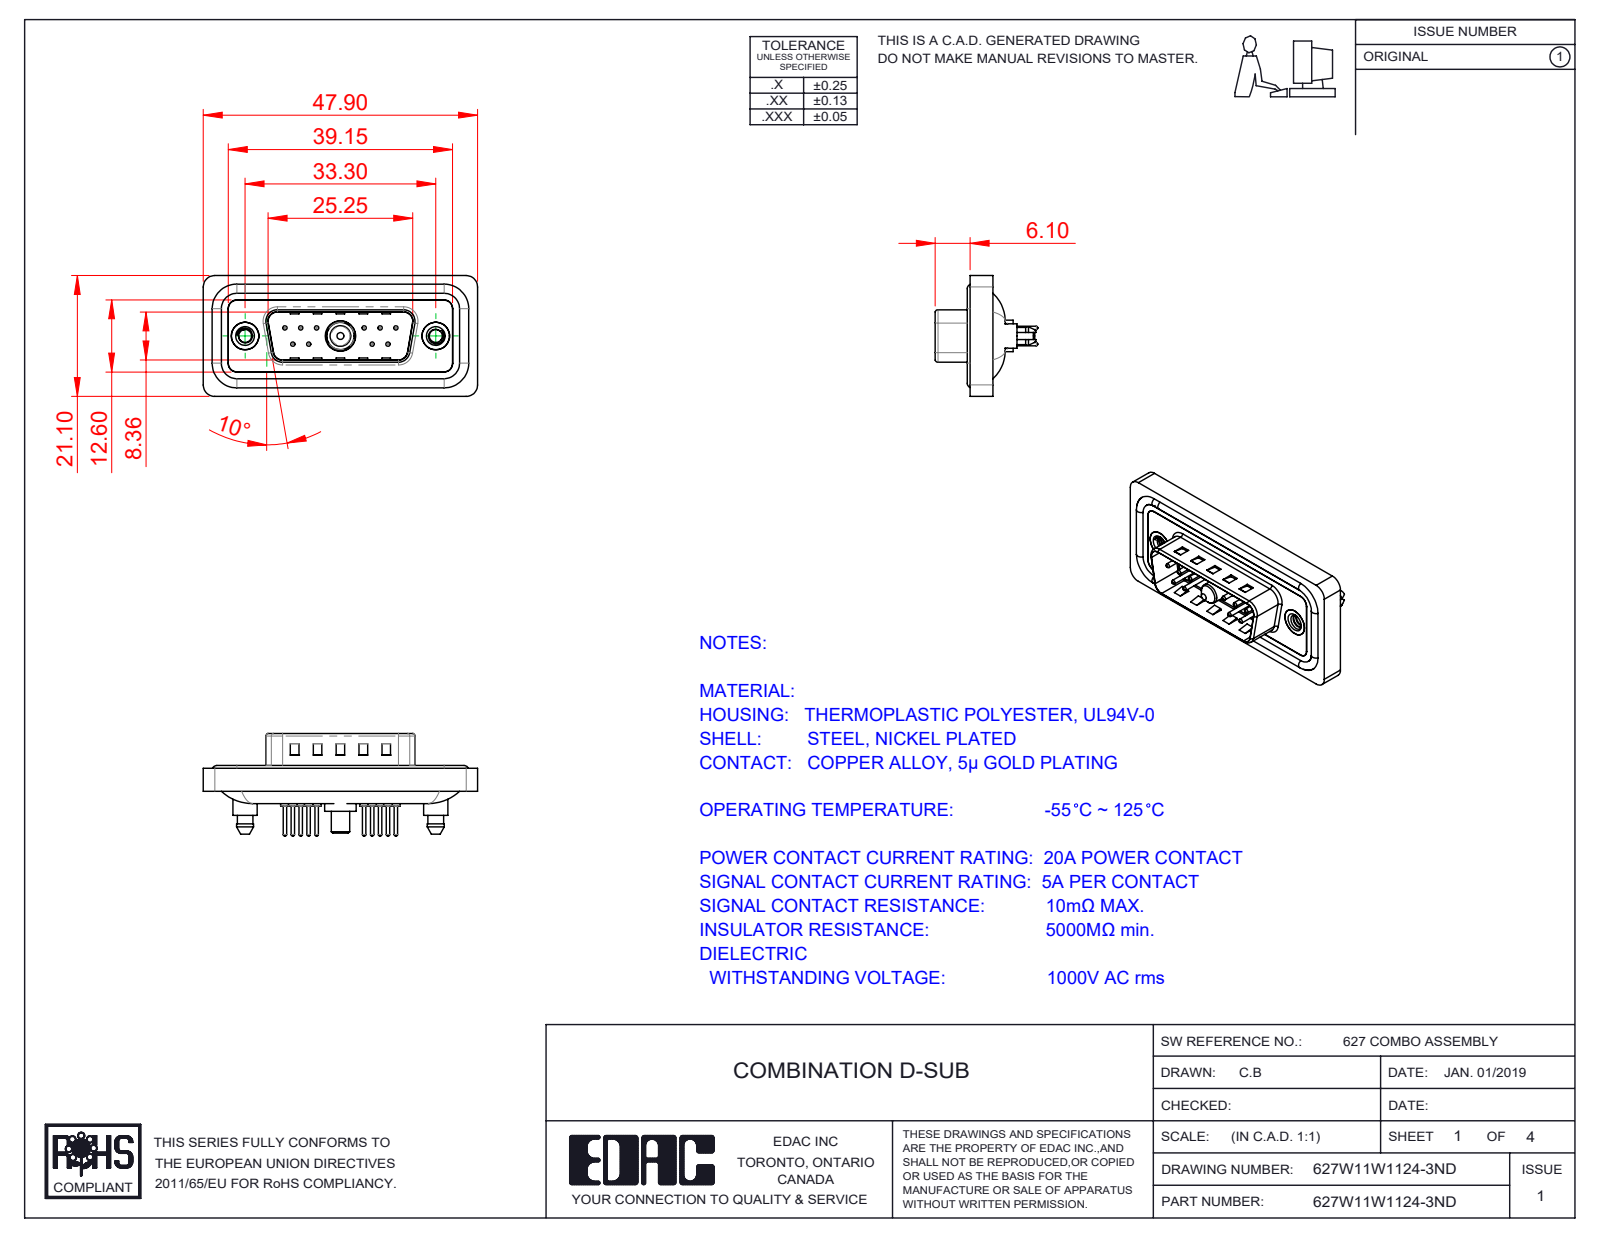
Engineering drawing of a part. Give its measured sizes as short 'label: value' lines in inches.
name: 627Combo Housing_11W1; 627W11W1124-3ND; 627Combo Shell Rear_15 Contacts; 627Combo Contact Row 2_24 (+6 more)
written by: SolidWorks 2020 (CONFIG_CONTROL_DESIGN)
unit: in
bodies: 19 solids, 927 faces (282 planar, 387 cylindrical, 258 other)
size: 1.886 × 0.831 × 0.705
volume: 0.341 in³; area: 14.22 in²
holes: 10× ⌀0.03, 10× ⌀0.063, 10× ⌀0.079, 2× ⌀0.089, 2× ⌀0.157, 2× ⌀0.189, 2× ⌀0.197, 1× ⌀0.191, 1× ⌀0.209
bosses: 10× ⌀0.059, 10× ⌀0.024, 4× ⌀0.063, 2× ⌀0.213, 2× ⌀0.193, 2× ⌀0.167, 1× ⌀0.217, 1× ⌀0.205
rounds: 28× R0.059, 20× R0.079, 10× R0.063, 8× R0.02, 7× R0.039, 4× R0.01, 4× R0.024, 4× R0.026
face distances: 0.016, 0.043, 0.063, 0.059, 0.114, 0.02, 0.122, 0.161, 0.032, 0.377
hole spacings: 0.124, 0.109, 0.545, 0.436, 0.654, 0.198, 0.198, 0.218
